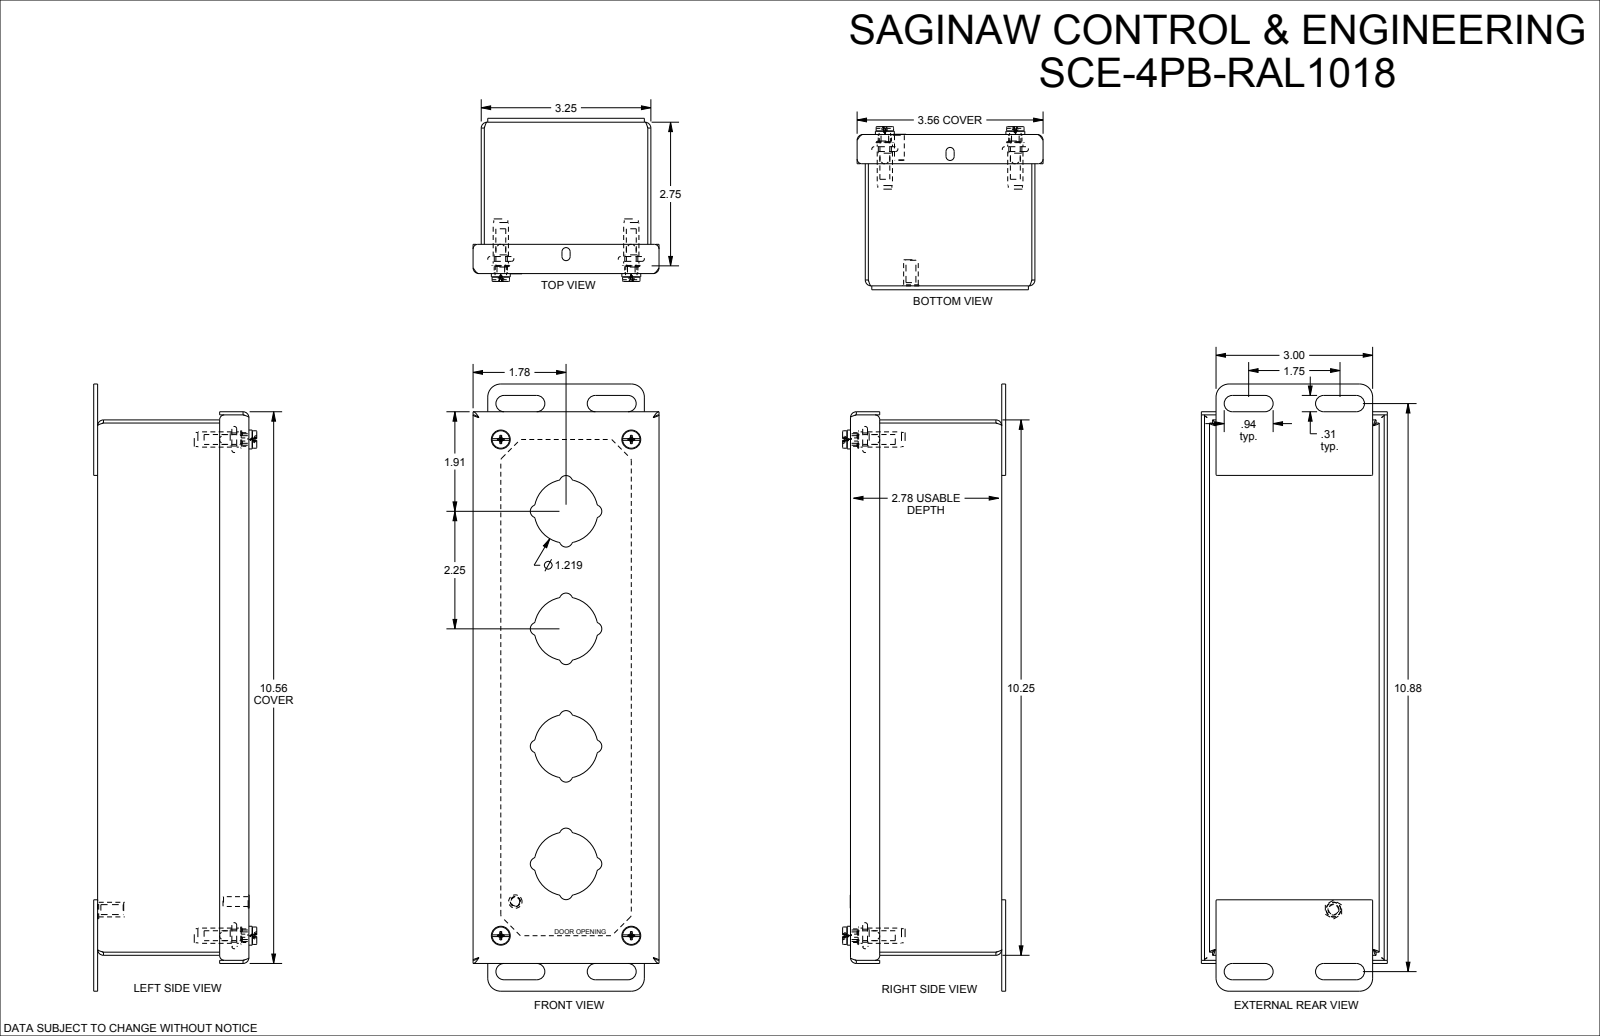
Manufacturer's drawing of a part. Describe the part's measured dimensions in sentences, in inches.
The part is named "SCE-4PB-RAL1018". Its 3-D file was written by "SolidWorks 2021 (AUTOMOTIVE_DESIGN)". It is 19 solids with 583 faces: 209 planar, 212 cylindrical and 162 other. Overall it measures 11.625 by 3.56 by 3.124 inches. Its volume is 11.08 cubic inches and its surface area 369.3 square inches. Round holes: 5 of diameter 0.19, 4 of diameter 0.22, 4 of diameter 0.25, 4 of diameter 0.25, 4 of diameter 0.317. Round bosses or shafts: 5 of diameter 0.188, 4 of diameter 0.437, 4 of diameter 0.362, 4 of diameter 0.34, 4 of diameter 0.334, 4 of diameter 0.292, 4 of diameter 0.27, 4 of diameter 0.26. Partial cylindrical surfaces (rounded edges, fillets, slot ends): 32 of radius 0.04, 16 of radius 0.125, 12 of radius 0.06, 8 of radius 0.015, 8 of radius 0.063, 8 of radius 0.115, 8 of radius 0.156, 8 of radius 0.245. The main face-to-face distances are 0.06, 2.838, 3.19, 2.778, 2.898, 3.25, 3.13, 10.19, 2.69, 0.148. The hole center spacings are 9.5, 9.824, 2.5, 9.497, 2.497, 2.5, 9.82, 2.498.
